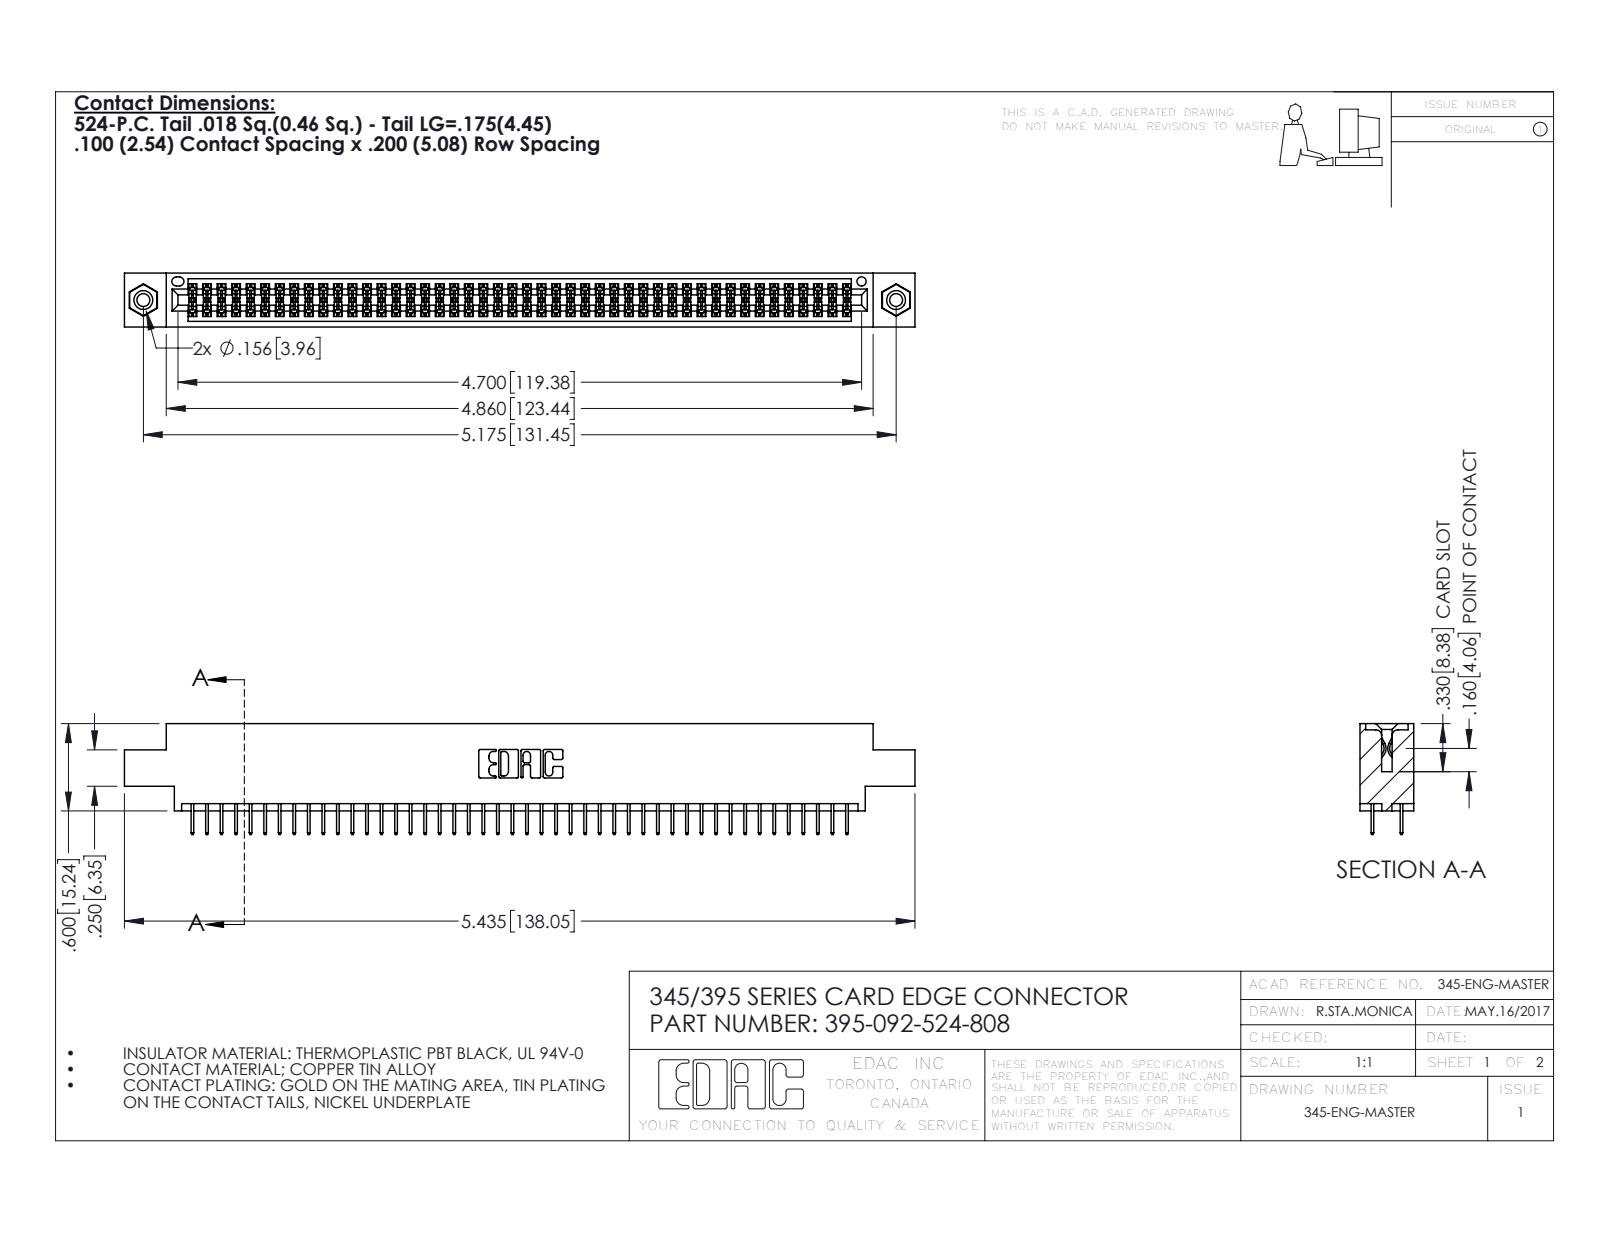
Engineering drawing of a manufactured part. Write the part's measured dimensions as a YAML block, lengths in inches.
part_name: "345-292-001_345-293-124; 345-250-001_345-250-003-102; 345 Part_0.170 Offset - 0.156 Dia-TI; 395-092-524-808"
step_written_by: "SolidWorks 2016 (CONFIG_CONTROL_DESIGN)"
units: inches
bodies: {solids: 95, faces: 5158, planar: 3704, cylindrical: 1438, other: 16}
overall_size: [5.435, 0.762, 0.37]
volume: 0.805
surface_area: 30.01
round_holes:
  - {diameter: 0.089, count: 2}
  - {diameter: 0.125, count: 2}
  - {diameter: 0.156, count: 2}
  - {diameter: 0.064, count: 1}
round_bosses_or_shafts:
  - {diameter: 0.155, count: 2}
partial_cylinders:
  - {radius: 0.006, count: 138}
  - {radius: 0.01, count: 22}
  - {radius: 0.007, count: 6}
  - {radius: 0.031, count: 6}
  - {radius: 0.026, count: 3}
  - {radius: 0.014, count: 2}
  - {radius: 0.019, count: 2}
  - {radius: 0.022, count: 2}
face_to_face_distances: [0.072, 0.298, 0.37, 0.2, 0.098, 0.272, 0.025, 0.225, 0.175, 0.072]
hole_center_spacings: [0.27, 4.939, 5.175]
